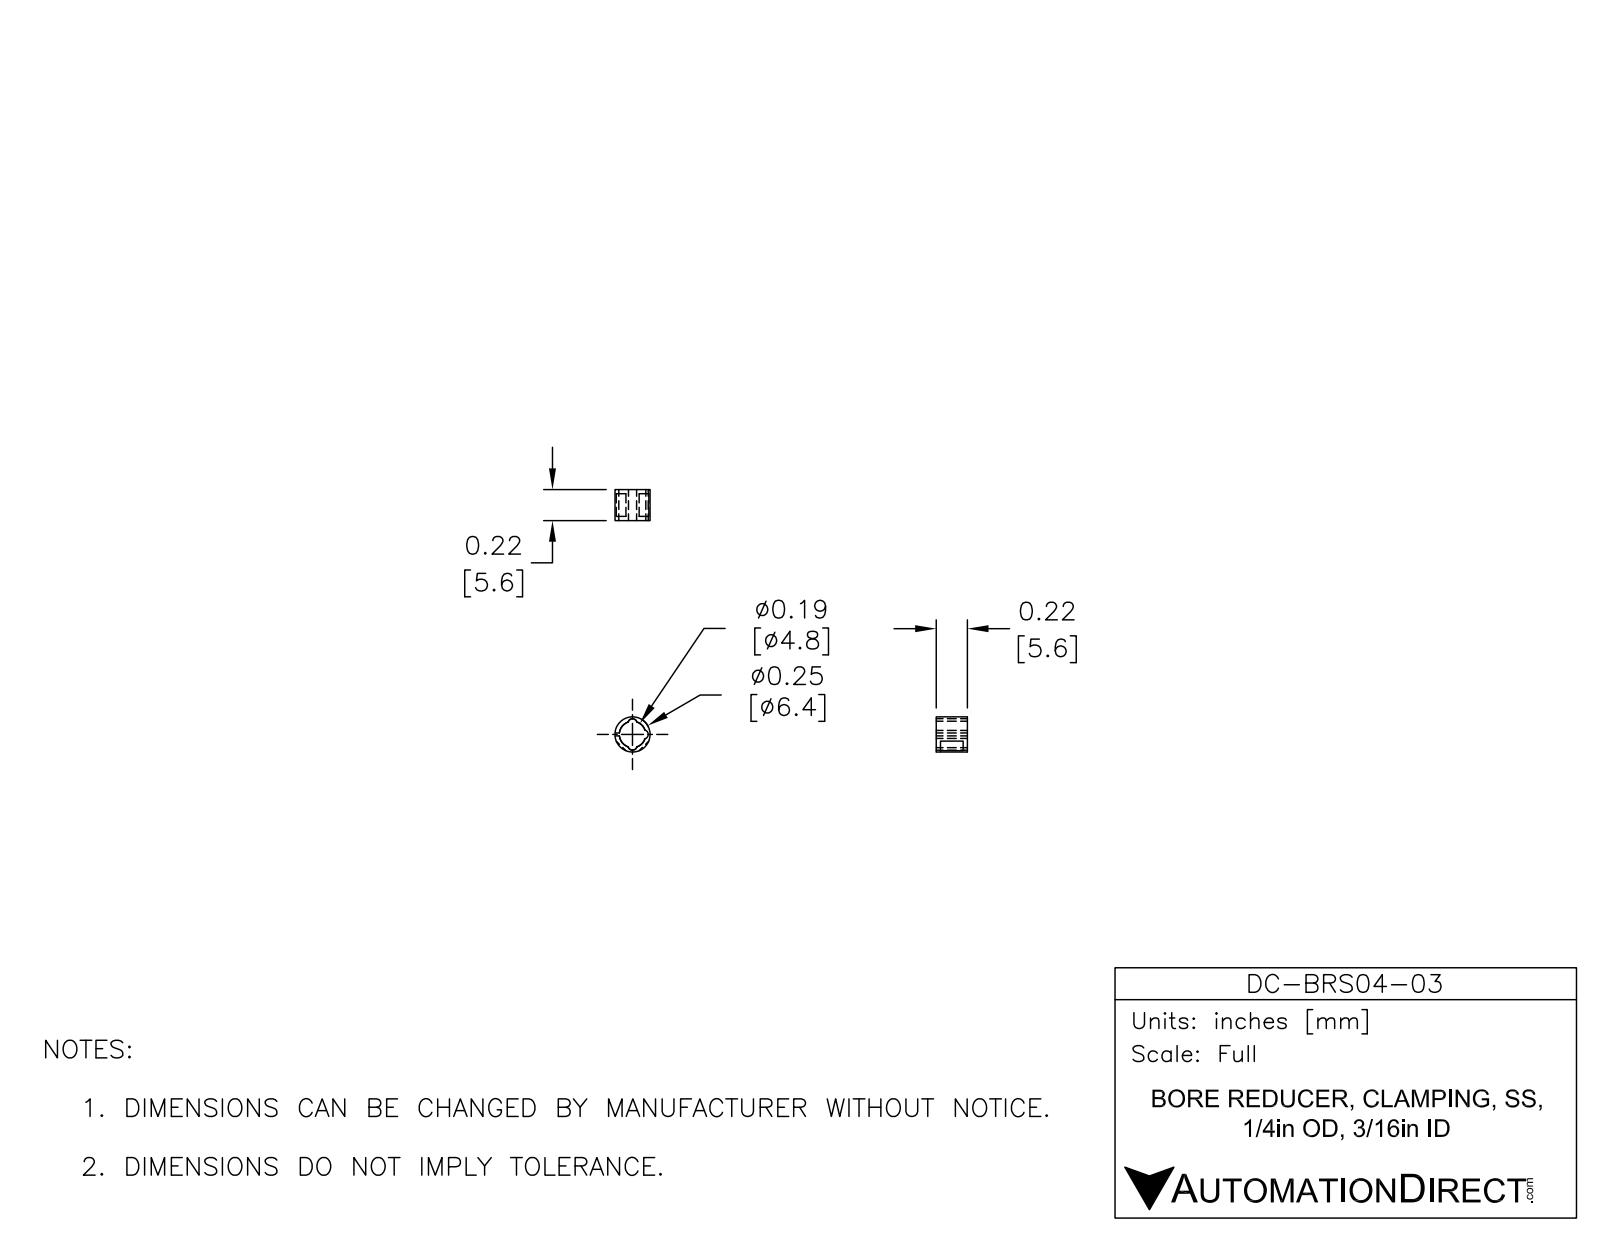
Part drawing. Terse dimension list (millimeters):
name: DC-BRS04-03
written by: SolidWorks 2015 (AUTOMOTIVE_DESIGN)
unit: mm
bodies: 1 solid, 21 faces (10 planar, 11 cylindrical, 0 other)
size: 6.35 × 6.34 × 5.61
volume: 63 mm³; area: 233 mm²
bosses: 1× ⌀6.35
rounds: 3× R0.81, 1× R2.38
face distances: 5.62, 0.5, 0.77, 4.85, 4.08
